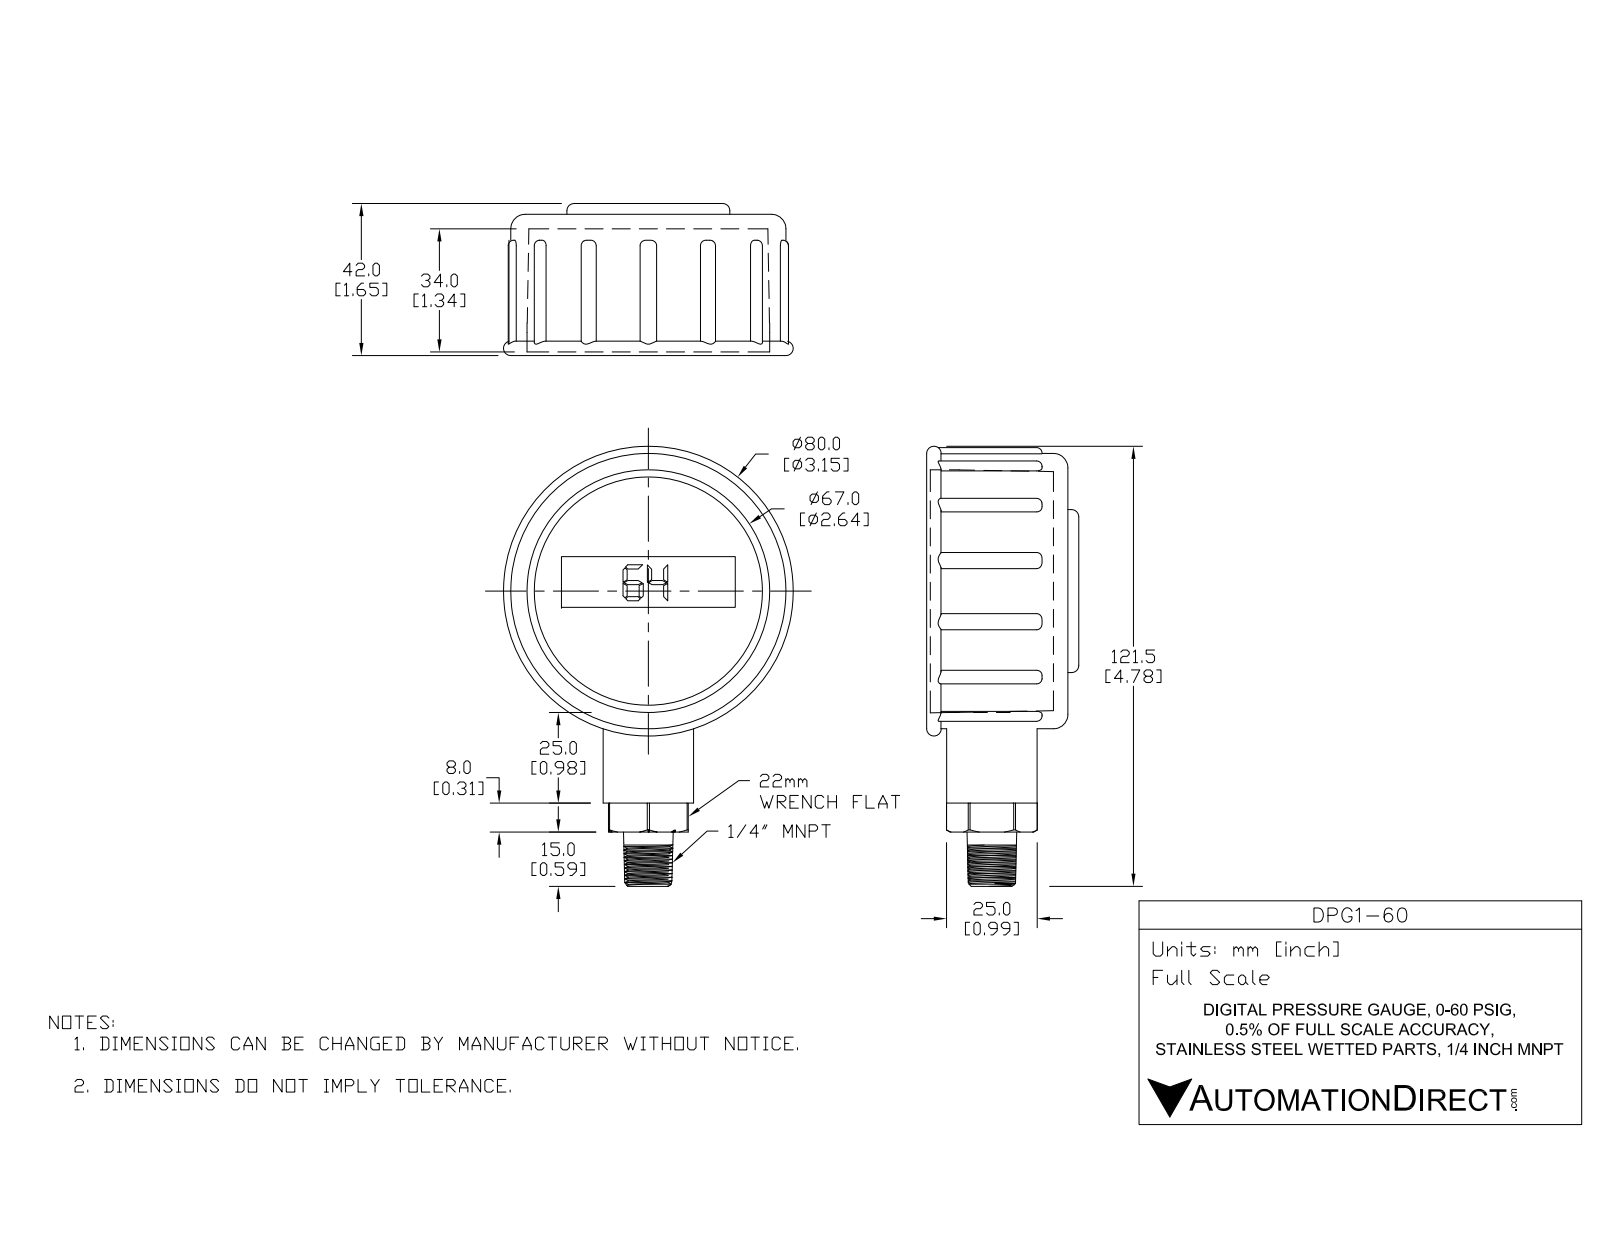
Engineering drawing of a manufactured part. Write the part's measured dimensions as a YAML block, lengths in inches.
part_name: "DPG1-60"
step_written_by: "SolidWorks 2021 (CONFIG_CONTROL_DESIGN)"
units: inches
bodies: {solids: 4, faces: 181, planar: 71, cylindrical: 49, other: 61}
overall_size: [4.788, 3.15, 1.654]
volume: 11.97
surface_area: 71.27
round_holes:
  - {diameter: 2.48, count: 1}
  - {diameter: 2.645, count: 1}
round_bosses_or_shafts:
  - {diameter: 2.992, count: 1}
  - {diameter: 2.638, count: 1}
  - {diameter: 1.772, count: 1}
  - {diameter: 0.984, count: 1}
  - {diameter: 0.394, count: 1}
partial_cylinders:
  - {radius: 0.094, count: 13}
  - {radius: 0.335, count: 6}
  - {radius: 1.496, count: 1}
face_to_face_distances: [1.337, 0.157, 1.494, 0.118, 0.276, 1.612, 1.654, 1.535, 1.378, 0.041]
